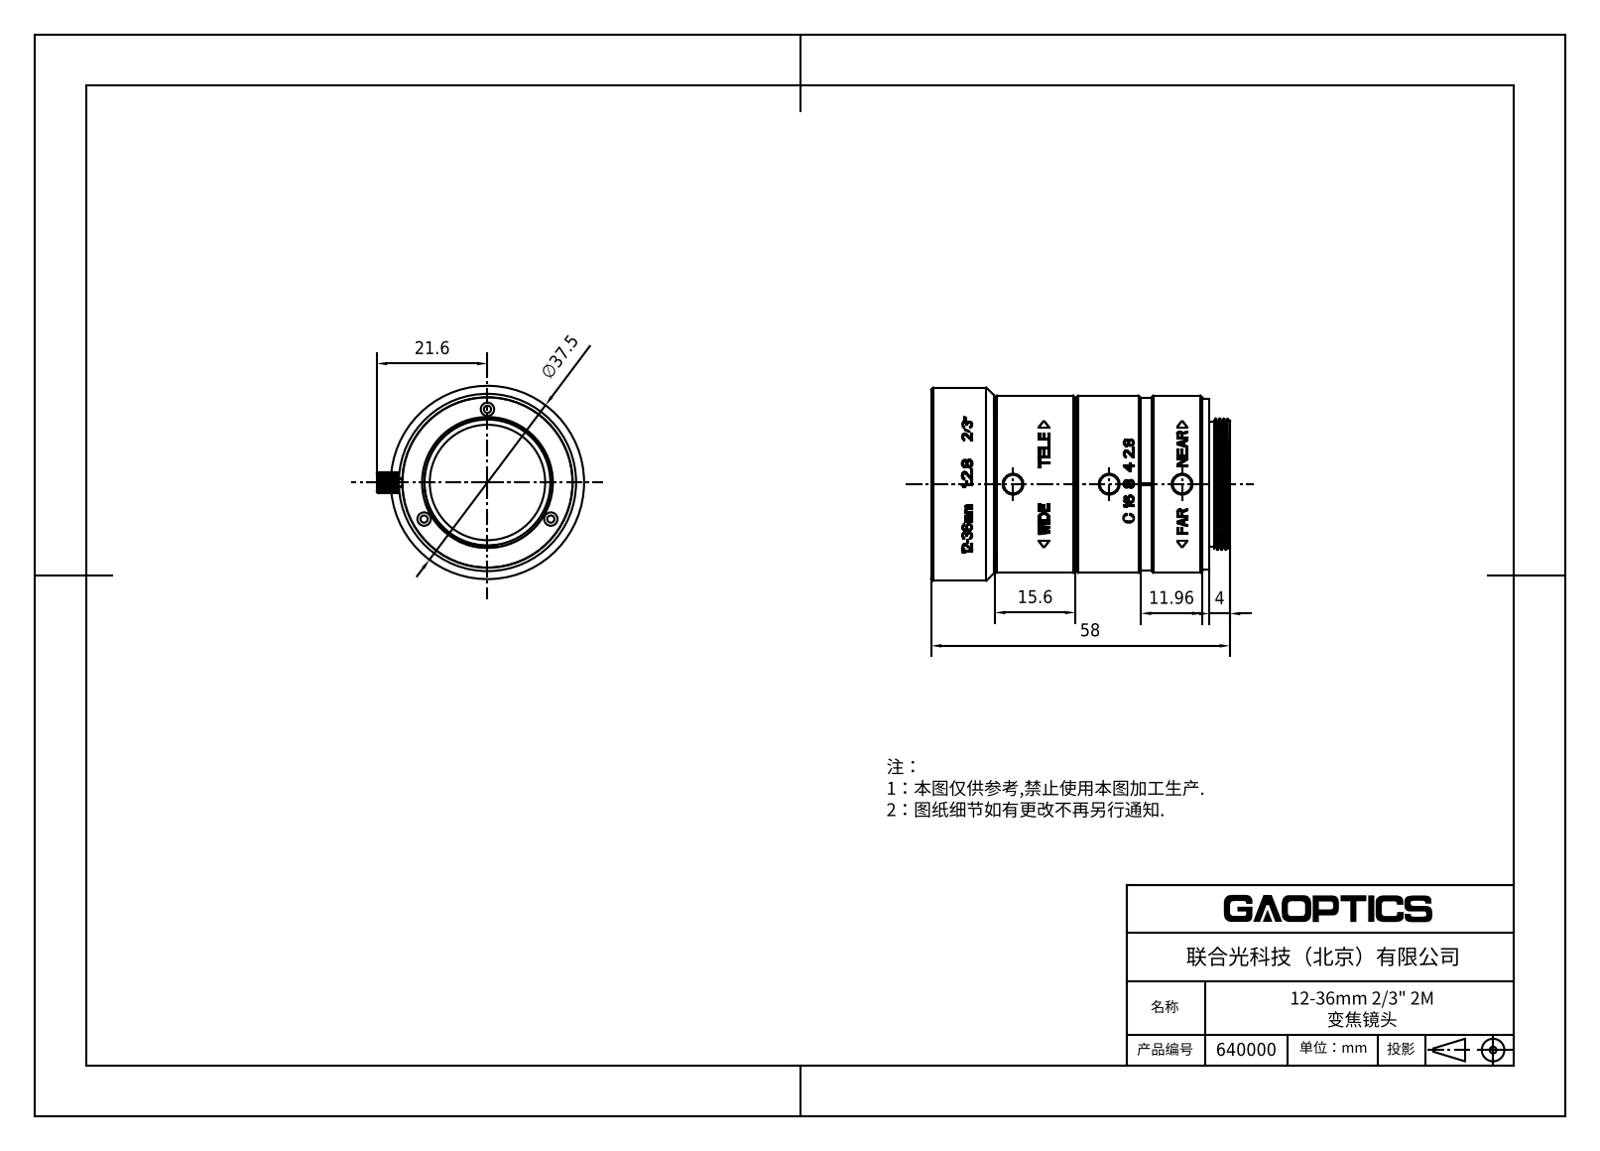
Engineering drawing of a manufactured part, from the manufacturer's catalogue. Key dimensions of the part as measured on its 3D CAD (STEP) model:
Part name (STEP PRODUCT): 640000
STEP written by: SolidWorks 2020 (CONFIG_CONTROL_DESIGN)
Units: millimetres
Bodies: 19 solids, 1761 faces (752 planar, 350 cylindrical, 659 other)
Overall size (bounding box): 58 × 40.35 × 37.5
Volume: 50 740 mm³ · Surface area: 25 947 mm²
Round holes (diameter × count): ⌀0.9 ×3, ⌀1.3 ×3, ⌀1.4 ×3, ⌀1.5 ×3, ⌀2.5 ×1, ⌀13.8 ×1, ⌀14.8 ×1, ⌀22.4 ×1, ⌀24 ×1, ⌀25 ×1, ⌀25.8 ×1, ⌀27.1 ×1
Round bosses / shafts (diameter × count): ⌀2 ×5, ⌀1.2 ×5, ⌀1.7 ×3, ⌀1.4 ×3, ⌀37.5 ×1, ⌀34.4 ×1, ⌀33.6 ×1, ⌀33 ×1
Partial cylindrical surfaces — rounded edges, fillets, slot ends (radius × count): R2 ×3, R1.75 ×2, R17.15 ×1, R17.17 ×1, R18.67 ×1, R18.7 ×1
Main face-to-face distances: 44.68, 4.83, 39.85, 1.3, 45.98, 41.15, 4, 51, 4.2, 49.98
Hole centre spacings: 14.2, 24.6, 4.42, 6.29, 6.39, 14.15, 14.25, 18.57
